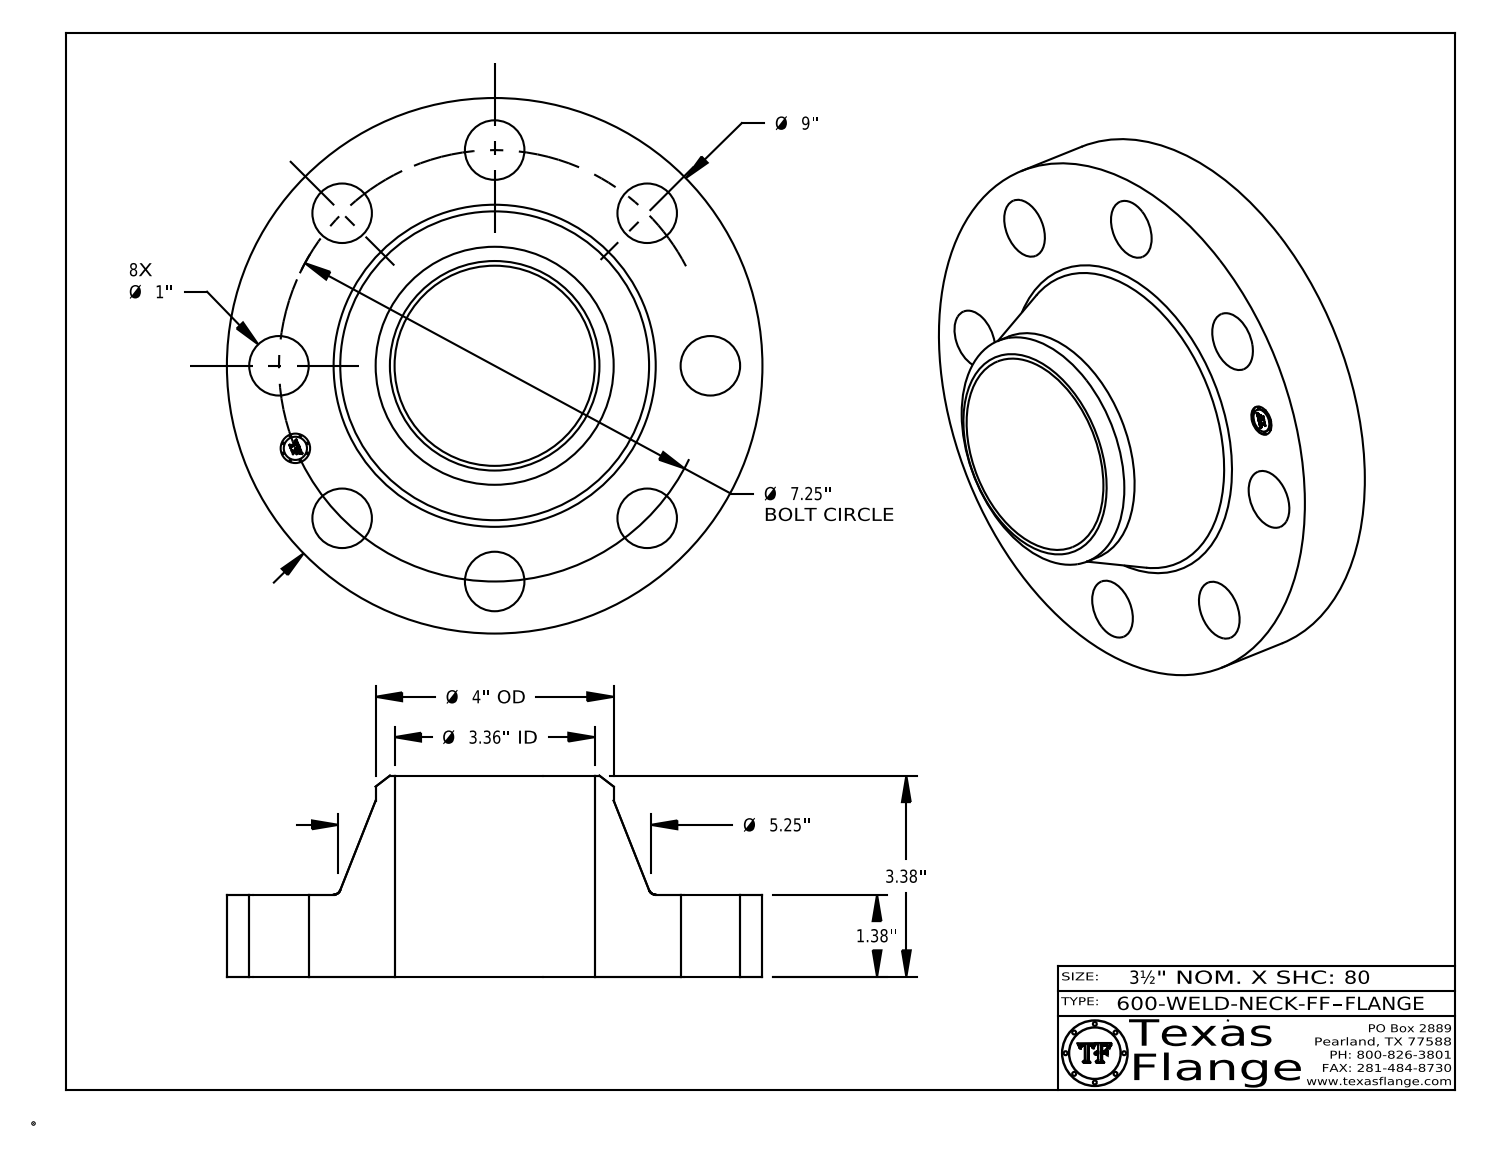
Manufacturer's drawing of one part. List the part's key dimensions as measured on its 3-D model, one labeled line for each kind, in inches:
Part name (STEP PRODUCT): 600-WELD-NECK-FF
STEP written by: CATIA V5 STEP AP214 (AUTOMOTIVE_DESIGN)
Units: inches
Bodies: 1 solid, 416 faces (368 planar, 42 cylindrical, 6 other)
Overall size (bounding box): 9 × 9 × 3.38
Volume: 80.82 in³ · Surface area: 225.4 in²
Round holes (diameter × count): ⌀1 ×8, ⌀0.495 ×1, ⌀3.364 ×1
Round bosses / shafts (diameter × count): ⌀0.03 ×8, ⌀9 ×1, ⌀4 ×1, ⌀0.39 ×1
Main face-to-face distances: 1.38, 3.38, 2, 1.365, 0.015, 2.015, 0.148, 0.144, 0.027, 0.096
Hole centre spacings: 3.625, 2.774, 5.127, 6.698, 7.25, 1.415, 7.111, 4.028
